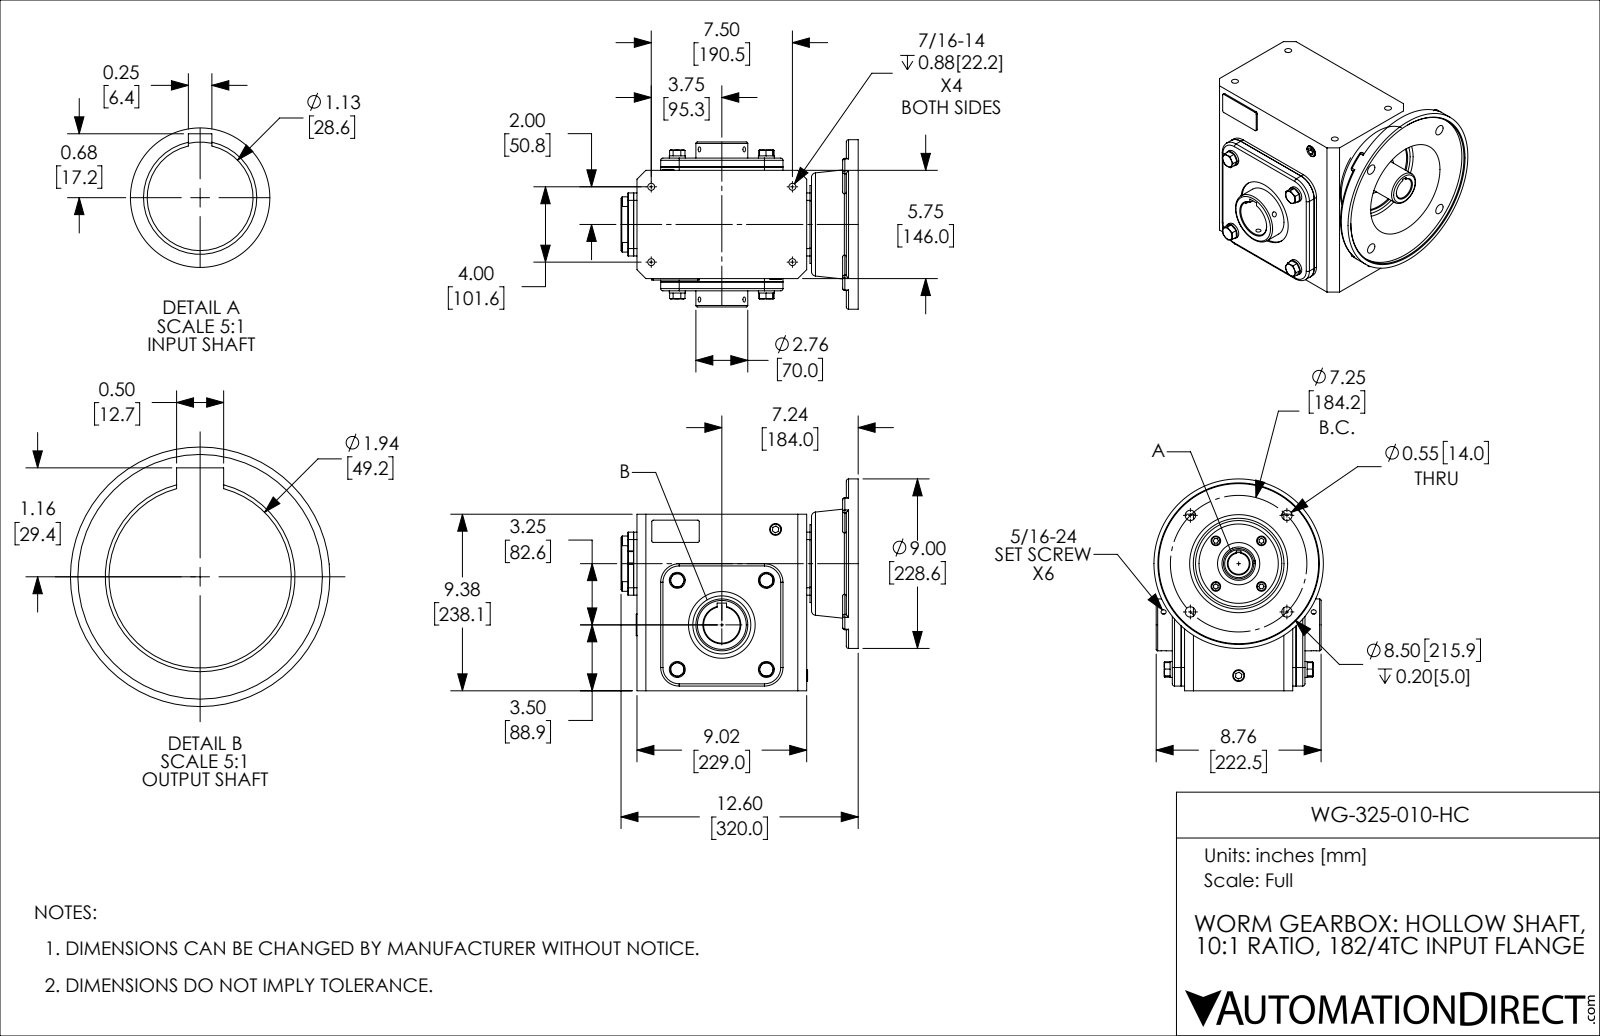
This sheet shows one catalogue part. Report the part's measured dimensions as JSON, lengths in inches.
{"part_name": "WG-325-010-HC", "step_written_by": "SolidWorks 2017 (AUTOMOTIVE_DESIGN)", "units": "inches", "bodies": {"solids": 40, "faces": 665, "planar": 332, "cylindrical": 206, "other": 127}, "overall_size": [12.598, 11.25, 9], "volume_in3": 542, "surface_area_in2": 1111, "round_holes": [[0.272, 6], [0.354, 4], [0.368, 4], [0.551, 4], [0.628, 3], [0.591, 1], [0.978, 1], [1.125, 1], [1.181, 1], [1.937, 1], [2.244, 1], [2.441, 1]], "round_bosses_or_shafts": [[0.846, 4], [0.512, 4], [9, 1], [4.134, 1], [2.835, 1], [1.772, 1], [1.142, 1]], "partial_cylinders_radius": [[0.118, 18], [0.079, 7], [0.394, 4], [0.906, 4], [0.984, 4], [0.02, 2], [0.039, 2]], "face_to_face_distances": [0.079, 0.177, 6.496, 0.394, 0.571, 6.319, 5.925, 6.398, 0.65, 0.472], "hole_center_spacings": [4.009, 1.713, 1.913, 2.422, 3.625, 4.244, 5.127, 5.338]}
